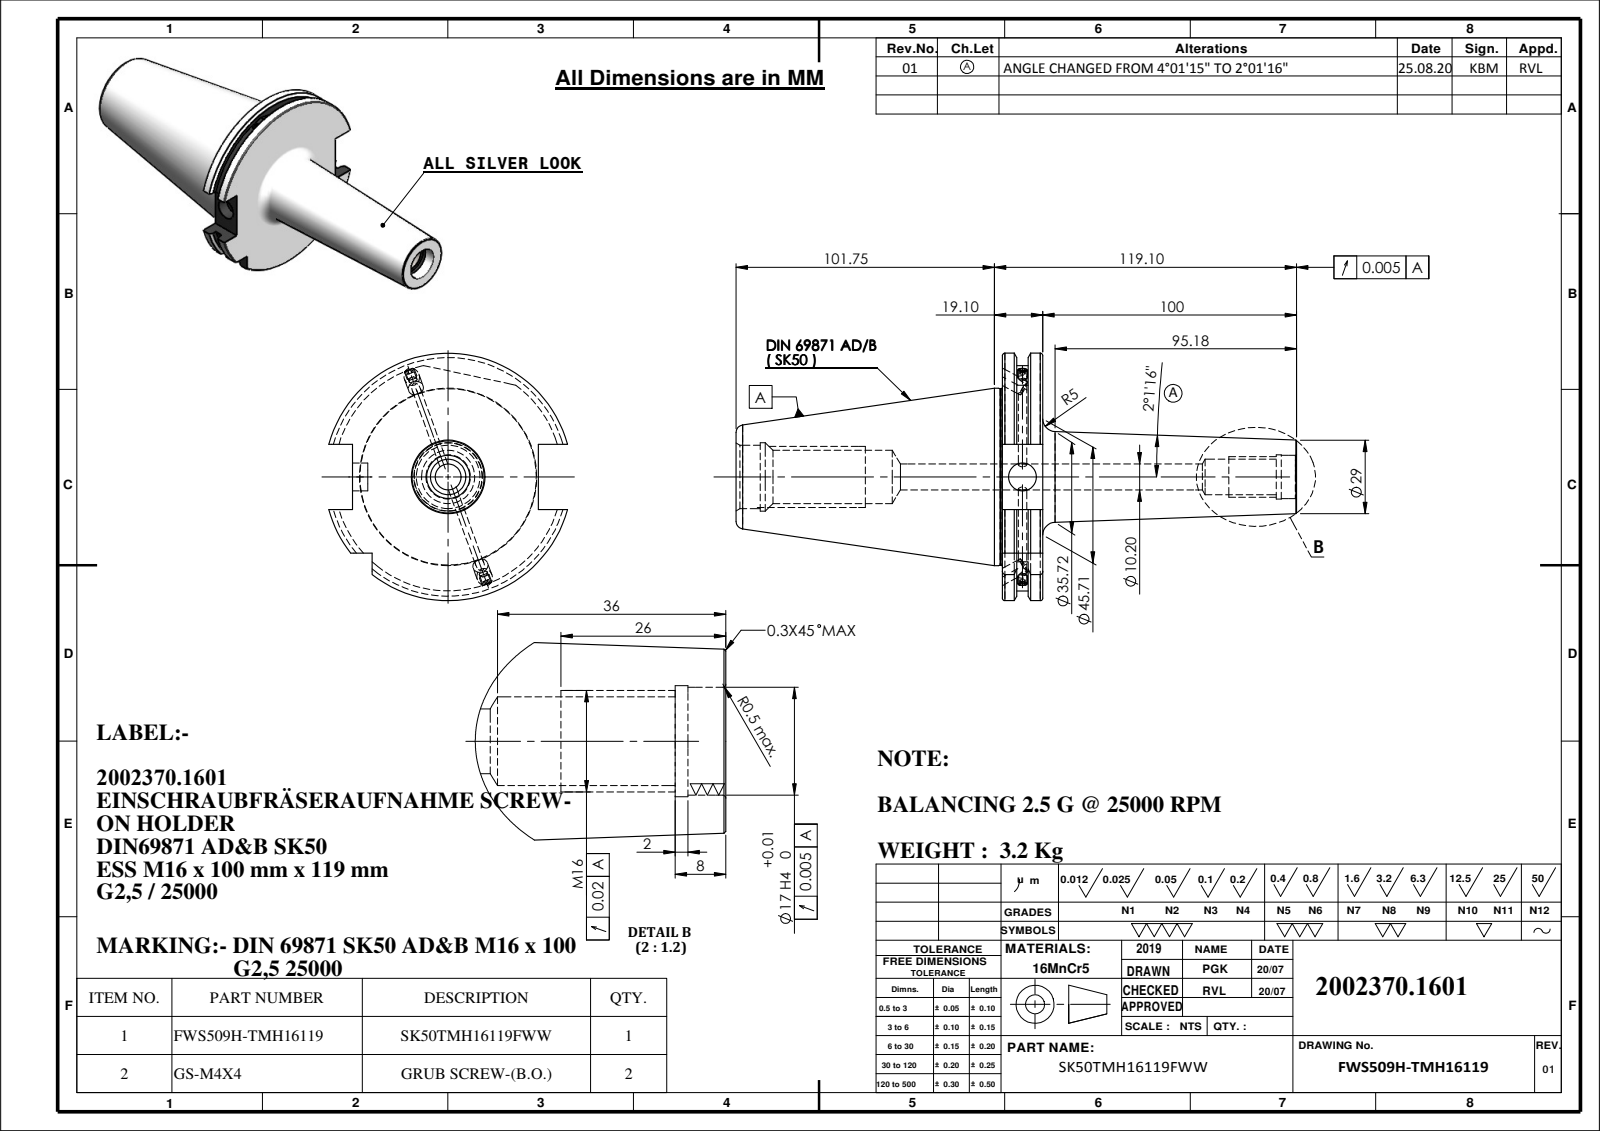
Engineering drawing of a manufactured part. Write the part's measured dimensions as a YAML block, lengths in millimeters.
part_name: "91506-ES7M16100; M4X4_DIN 913 - M4 x 4-N; SK50TMH16119FWW"
step_written_by: "SolidWorks 2018 (AUTOMOTIVE_DESIGN)"
units: millimeters
bodies: {solids: 3, faces: 142, planar: 43, cylindrical: 49, other: 50}
overall_size: [220.85, 97.5, 94.05]
volume: 405616
surface_area: 56888
round_holes:
  - {diameter: 6, count: 2}
  - {diameter: 3.3, count: 1}
  - {diameter: 10.2, count: 1}
  - {diameter: 11, count: 1}
  - {diameter: 14, count: 1}
  - {diameter: 17, count: 1}
  - {diameter: 17.5, count: 1}
  - {diameter: 21, count: 1}
  - {diameter: 25, count: 1}
  - {diameter: 27, count: 1}
round_bosses_or_shafts:
  - {diameter: 4, count: 2}
  - {diameter: 69.85, count: 1}
  - {diameter: 69.45, count: 1}
partial_cylinders:
  - {radius: 44.9, count: 1}
  - {radius: 48.75, count: 1}
face_to_face_distances: [15.9, 5.66, 10.24, 10.14, 4.48, 5.76, 104.95, 110.61, 115.09, 120.85]
